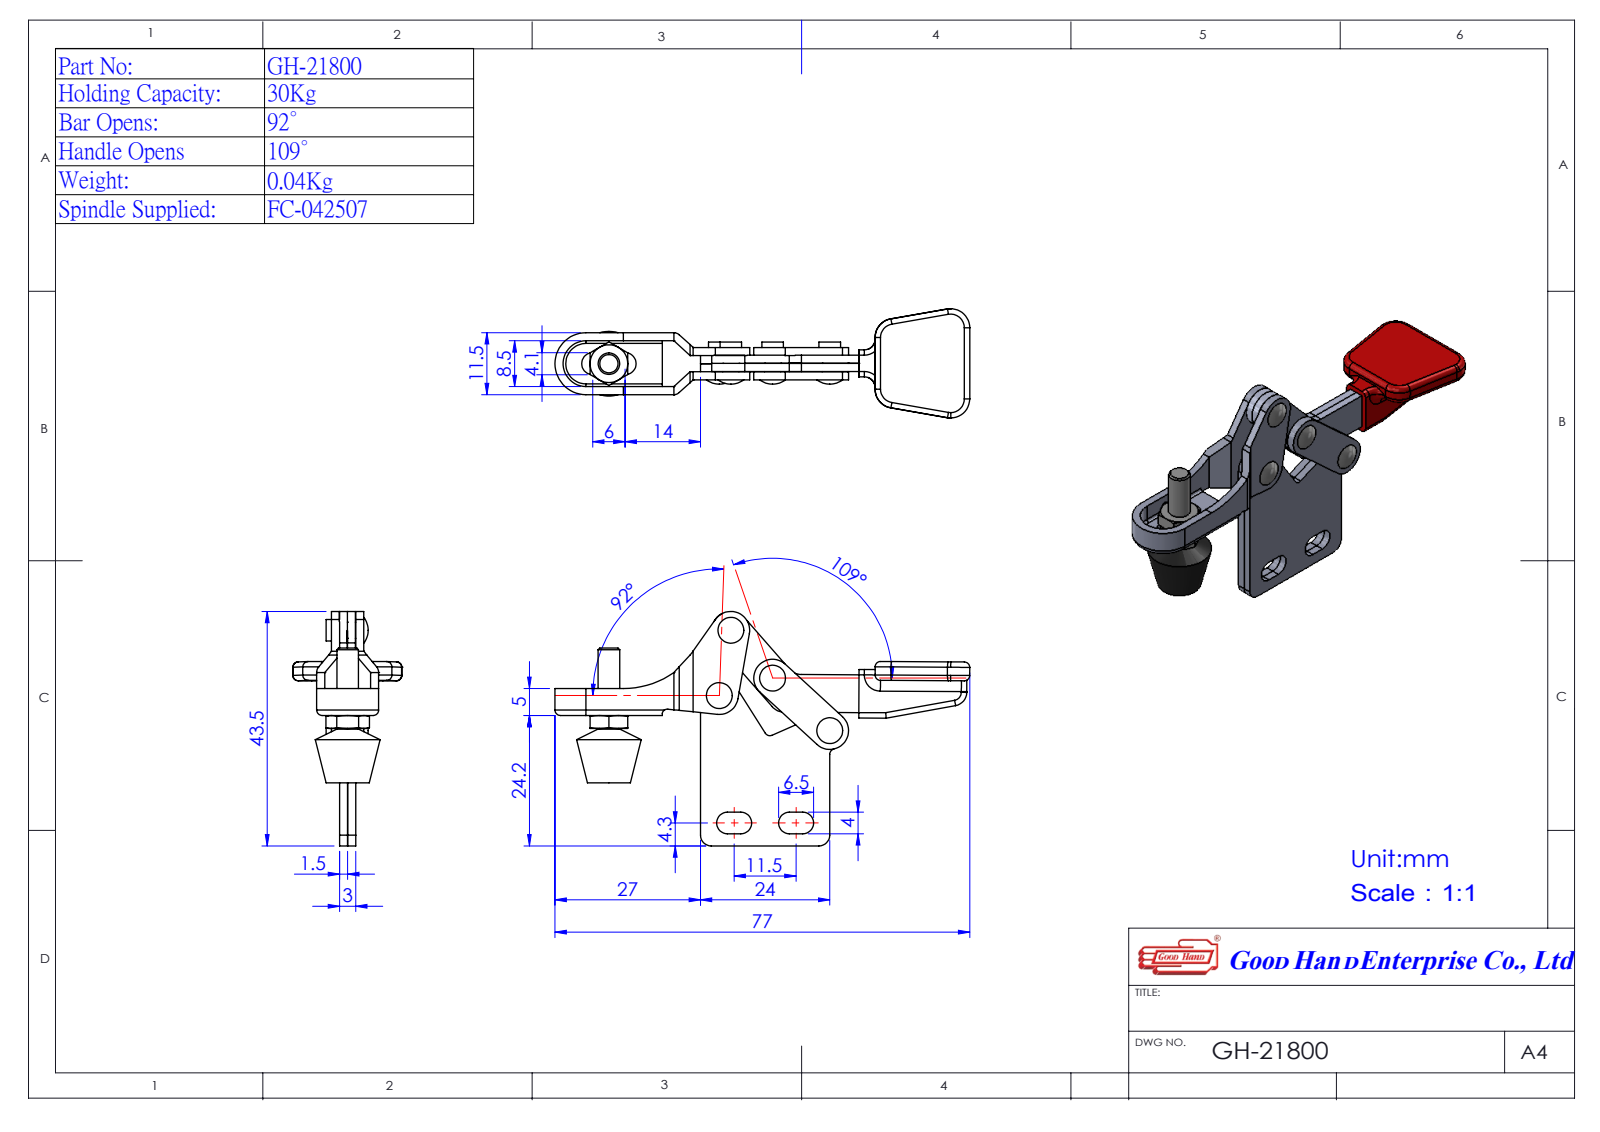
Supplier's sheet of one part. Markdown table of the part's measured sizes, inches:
| quantity | value |
| --- | --- |
| part name | 12080001-1^GH-21800(簡化)-1; Group1^GH-21800(簡化); Group3^GH-21800(簡化)-1; Group5^GH-21800(簡化)-1 (+2 more) |
| STEP written by | SolidWorks 2016 (AUTOMOTIVE_DESIGN) |
| units | inches |
| bodies | 5 solids, 242 faces (103 planar, 101 cylindrical, 38 other) |
| overall size | 3.033 × 1.713 × 0.798 |
| volume | 0.418 in³ |
| surface area | 11.36 in² |
| round holes (diameter × count) | 0.098 × 4 |
| round bosses / shafts (diameter × count) | 0.138 × 4, 0.157 × 1 |
| partial cylindrical surfaces (radius × count) | 0.079 × 8, 0.138 × 4, 0.139 × 4, 0.039 × 3, 0.118 × 2, 0.098 × 1, 0.138 × 1, 0.152 × 1 |
| main face-to-face distances | 0.059, 0.118, 0.177, 0.039, 0.108, 0.167, 0.226, 0.285, 0.157, 0.138 |
| hole center spacings | 0.41, 0.464, 0.484, 0.567, 0.847, 1.029 |
